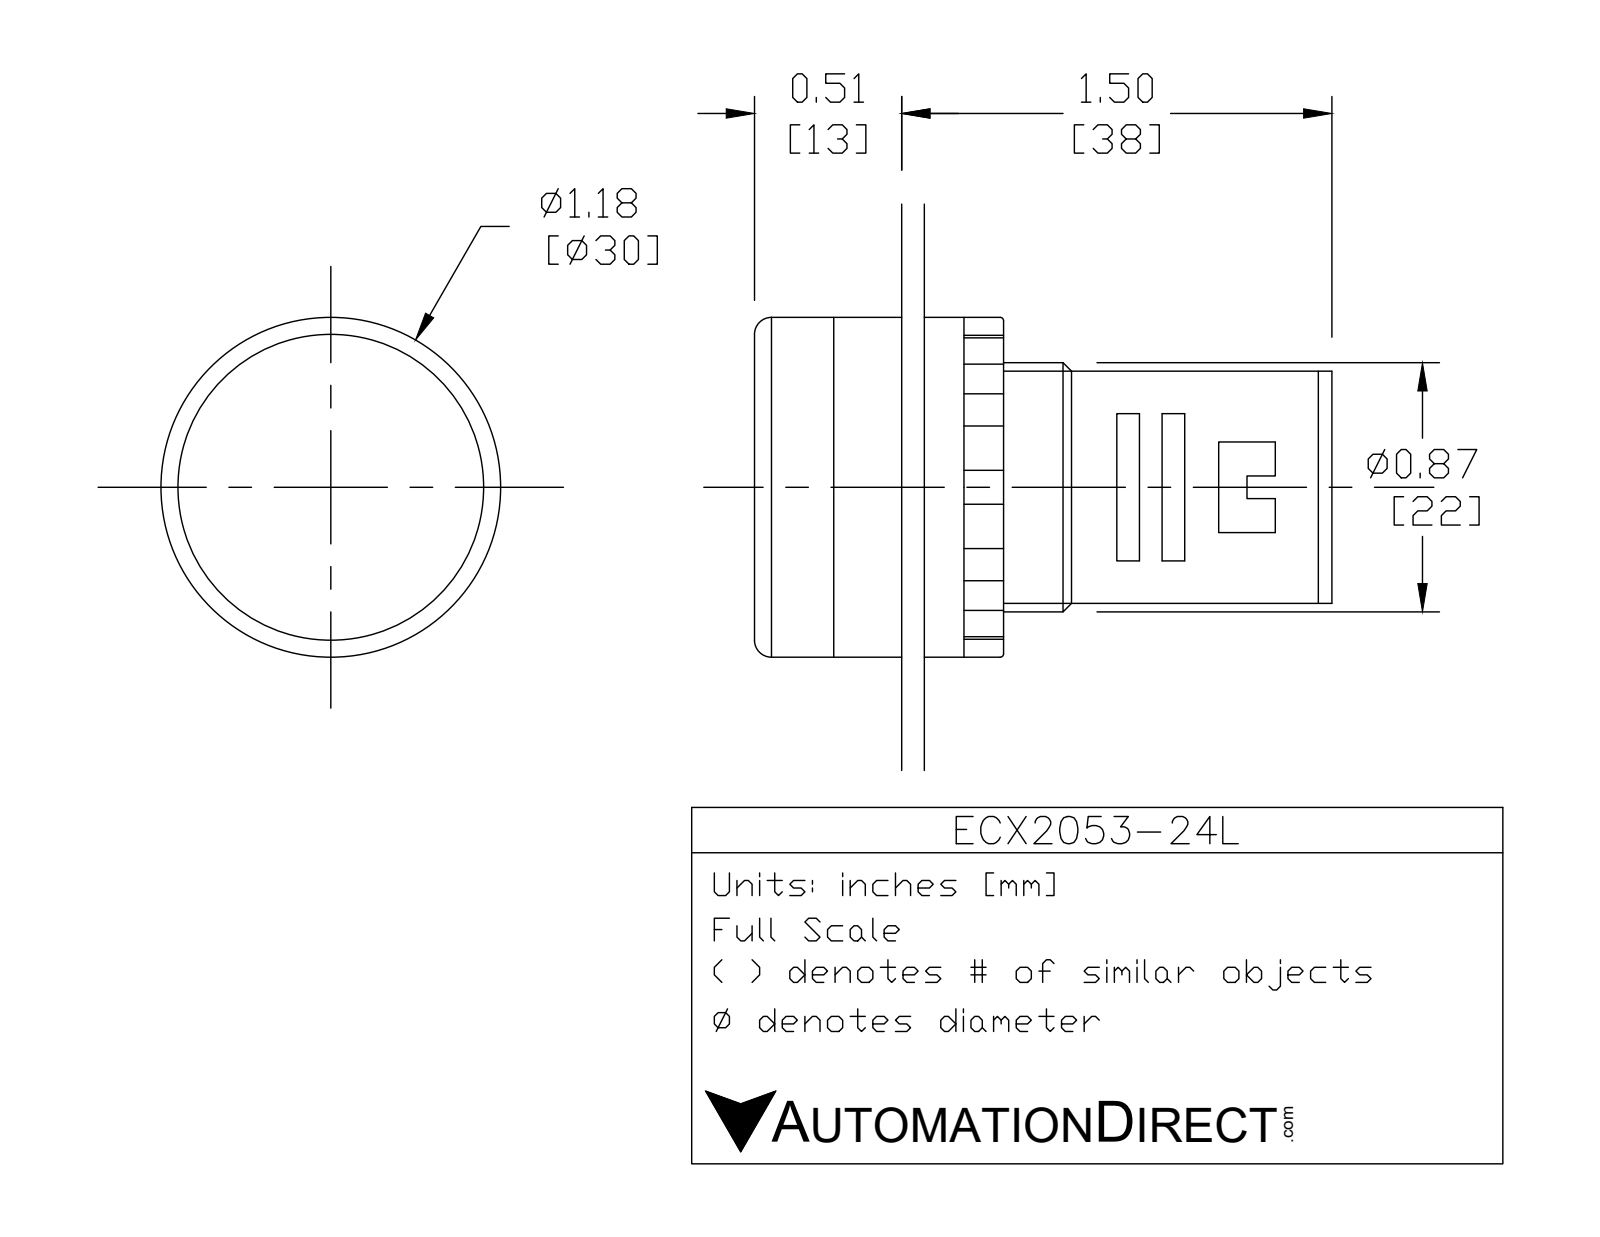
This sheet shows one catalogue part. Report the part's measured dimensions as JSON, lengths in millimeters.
{"part_name": "ECX2053-24L", "step_written_by": "SolidWorks 2017 (AUTOMOTIVE_DESIGN)", "units": "millimeters", "bodies": {"solids": 6, "faces": 123, "planar": 63, "cylindrical": 39, "other": 21}, "overall_size": [51, 30, 30], "volume_mm3": 22483, "surface_area_mm2": 9831, "round_holes": [[5.5, 2], [22.5, 1]], "round_bosses_or_shafts": [[4, 2], [30, 1], [29, 1], [26.5, 1], [22, 1], [20, 1]], "partial_cylinders_radius": [[1, 12]], "face_to_face_distances": [6, 19, 13, 7, 2, 25, 4, 12, 17, 15], "hole_center_spacings": [4.62, 9.24]}
